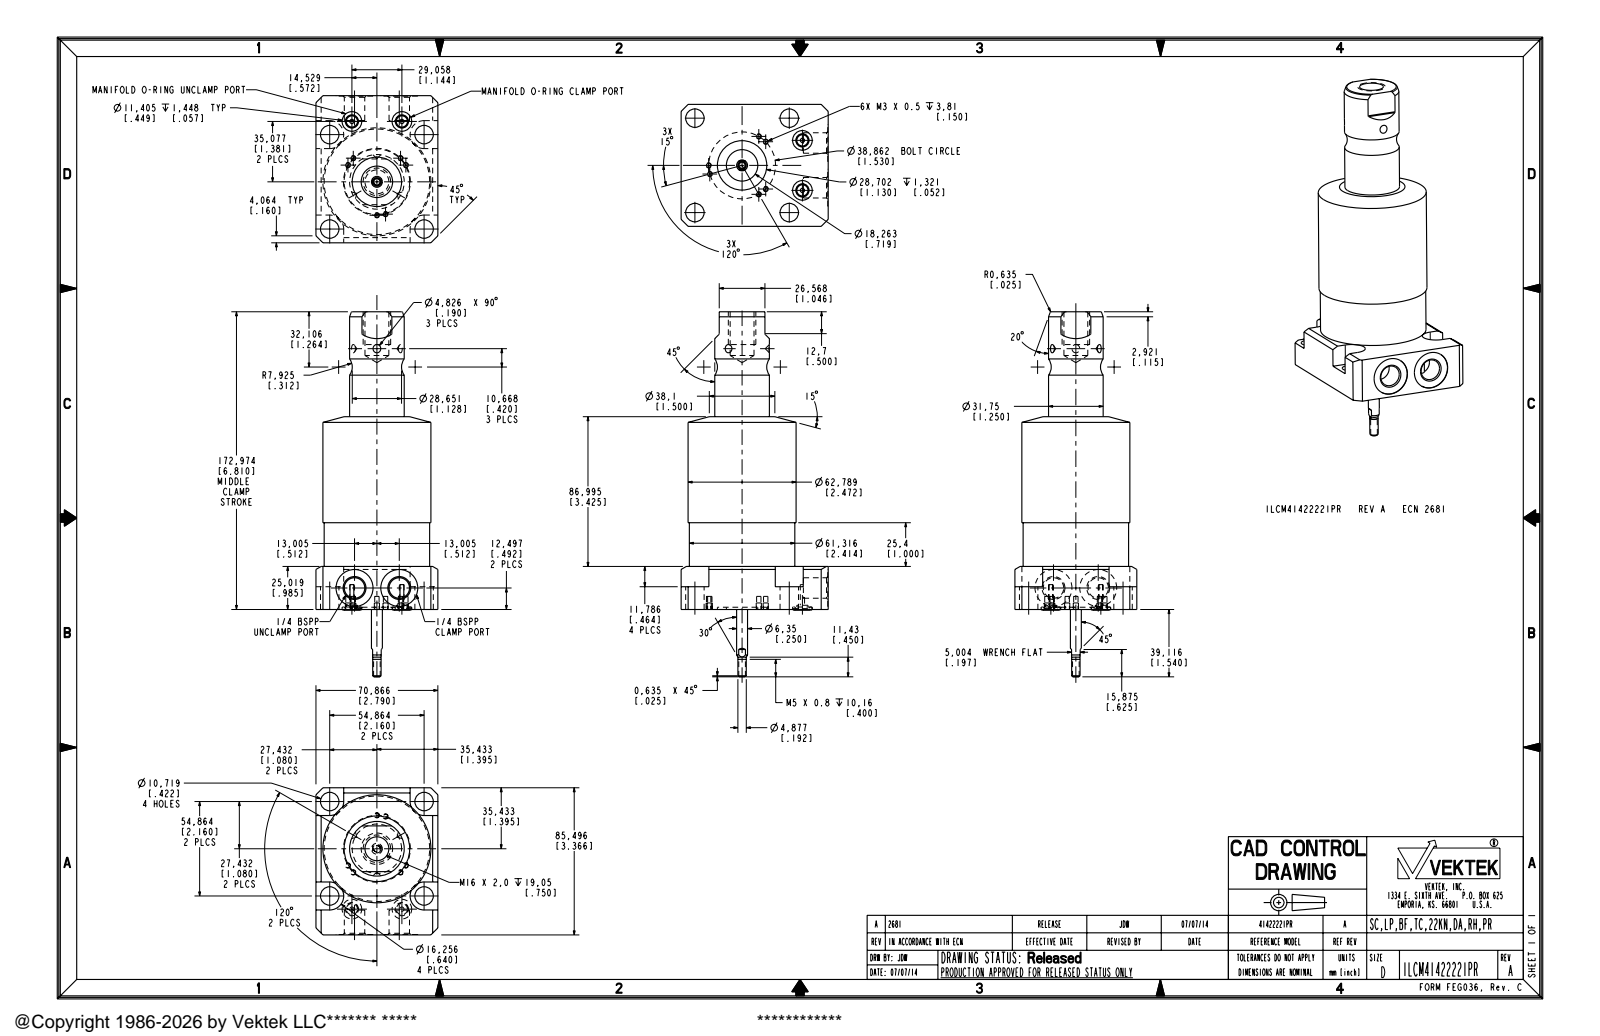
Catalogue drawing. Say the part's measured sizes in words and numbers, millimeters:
The part is named "ILCM41422221PR". Its 3-D file was written by "PRO/ENGINEER BY PARAMETRIC TECHNOLOGY CORPORATION, 2013320 (AUTOMOTIVE_DESIGN)". It is 1 solid with 182 faces: 68 planar, 82 cylindrical and 32 other. Overall it measures 212.09 by 85.5 by 70.87 millimeters. Its volume is 435 667 cubic millimeters and its surface area 49 204 square millimeters. Round holes: 6 of diameter 2.54, 4 of diameter 10.72, 2 of diameter 2.49, 2 of diameter 6.5, 2 of diameter 11.4, 2 of diameter 11.89, 2 of diameter 21.49, 1 of diameter 13.87, 1 of diameter 28.7. Round bosses or shafts: 6 of diameter 3, 1 of diameter 62.79, 1 of diameter 61.32, 1 of diameter 31.75, 1 of diameter 18.26, 1 of diameter 16, 1 of diameter 6.35, 1 of diameter 4.88. Partial cylindrical surfaces (rounded edges, fillets, slot ends): 4 of radius 8.13, 2 of radius 0.76. The main face-to-face distances are 25.02, 70.86, 85.49, 11.79, 13.23, 147.96, 159.75, 172.98, 85.24, 171.66. The hole center spacings are 19.43, 33.66, 38.79, 43.39, 54.86, 5.07, 15, 19.36.
